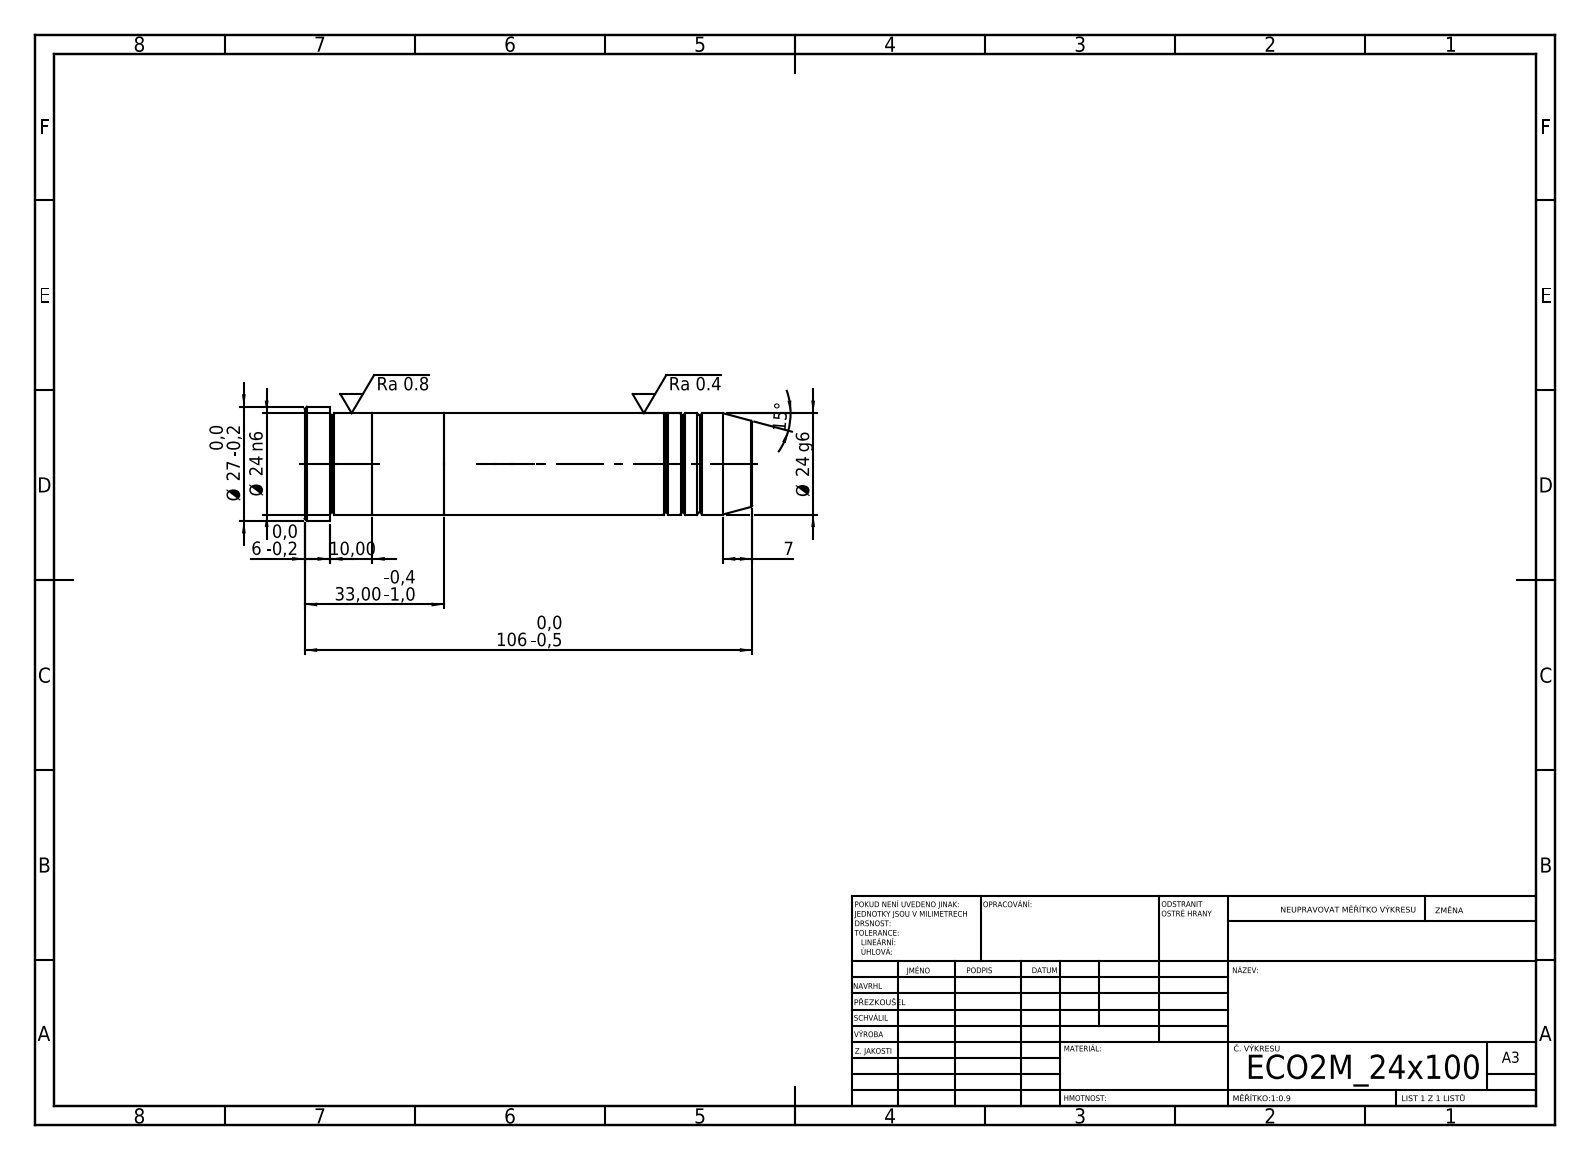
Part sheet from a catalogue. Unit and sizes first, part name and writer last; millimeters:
Units: millimetres
Overall size (bounding box): 106 × 27 × 27
Round bosses / shafts (diameter × count): ⌀27 ×1, ⌀24 ×1
Main face-to-face distances: 17, 33, 16, 73, 90, 106, 100, 27, 10, 6
Volume: 48 076 mm³ · Surface area: 10 976 mm²
Bodies: 3 solids, 43 faces (7 planar, 14 cylindrical, 22 other)
STEP written by: SolidWorks 2019 (CONFIG_CONTROL_DESIGN)
